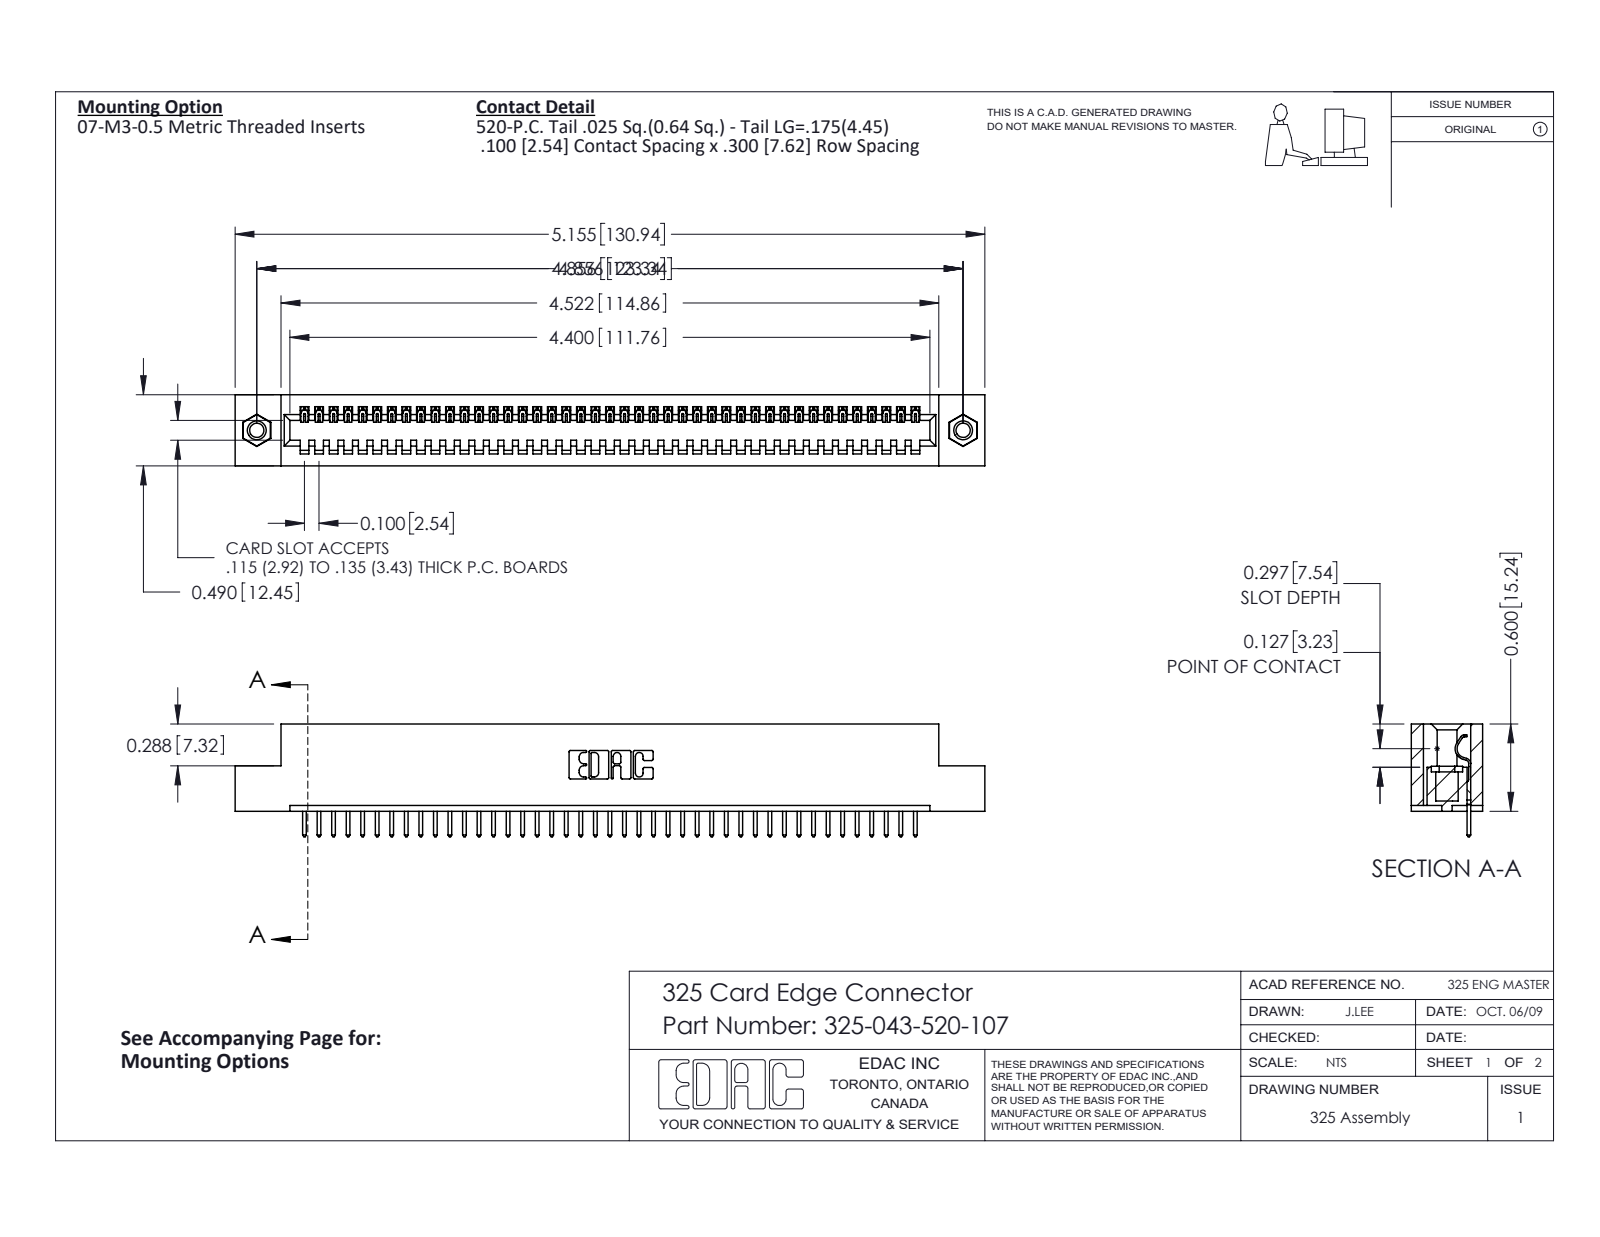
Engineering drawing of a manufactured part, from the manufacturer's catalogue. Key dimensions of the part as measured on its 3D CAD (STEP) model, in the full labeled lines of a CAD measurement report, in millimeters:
Part name (STEP PRODUCT): 325-043-520-107; 345-250-001_345-250-005-103; 325-292-001_325-293-120; 325 Part_TI
STEP written by: SolidWorks 2016 (CONFIG_CONTROL_DESIGN)
Units: millimetres
Bodies: 46 solids, 2668 faces (1908 planar, 744 cylindrical, 16 other)
Overall size (bounding box): 130.9 × 19.7 × 12.4
Volume: 16 500 mm³ · Surface area: 17 630 mm²
Round holes (diameter × count): ⌀2.5 ×2, ⌀3.2 ×2, ⌀4.1 ×2
Round bosses / shafts (diameter × count): ⌀3.9 ×2
Partial cylindrical surfaces — rounded edges, fillets, slot ends (radius × count): R0.2 ×86, R0.3 ×86, R0.3 ×22, R0.2 ×6, R0.8 ×6, R0.7 ×3, R0.4 ×1, R0.6 ×1
Main face-to-face distances: 2.1, 10.3, 12.4, 7.6, 2.7, 9.7, 0.6, 8.3, 14.2, 1
Hole centre spacings: 123.3
